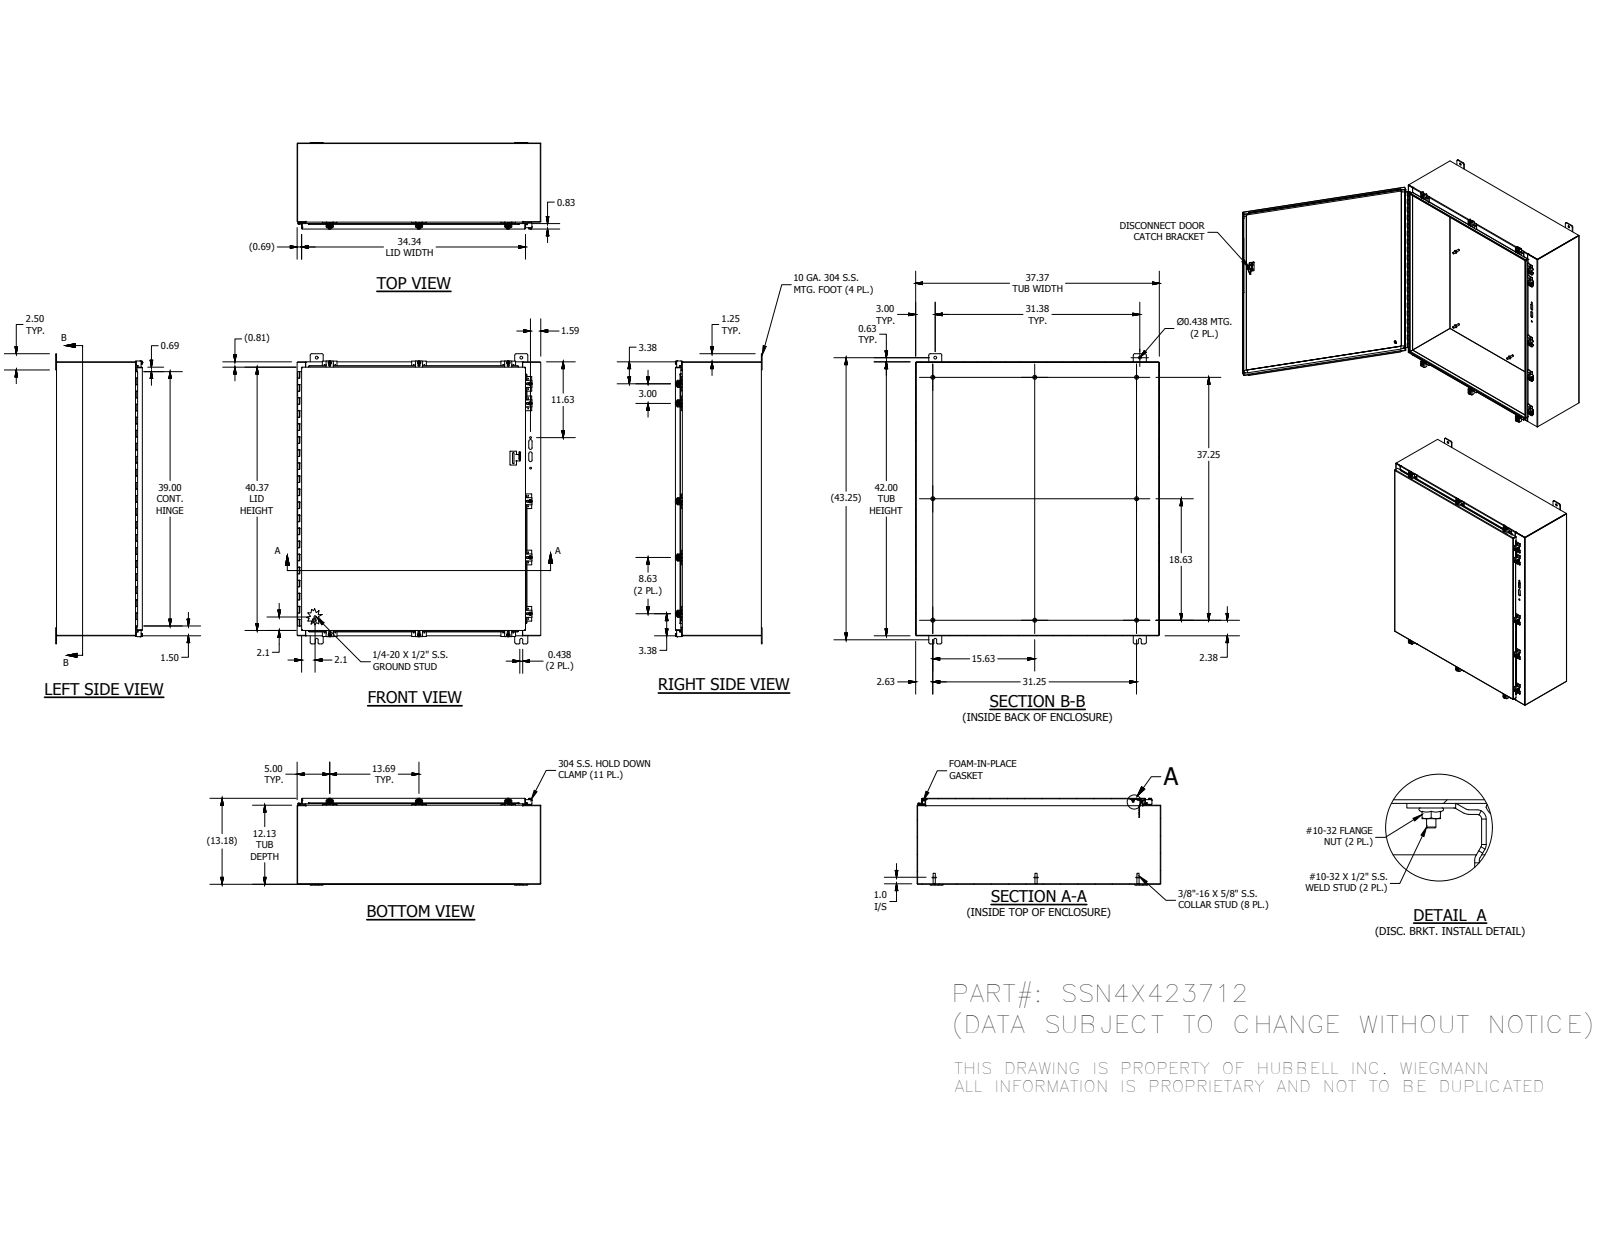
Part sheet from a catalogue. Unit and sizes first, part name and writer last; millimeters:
Units: millimetres
Overall size (bounding box): 1130.3 × 949.33 × 337.85
Round holes (diameter × count): ⌀2.79 ×22, ⌀5.36 ×11, ⌀7.16 ×11, ⌀11.13 ×4, ⌀3.96 ×2, ⌀7.14 ×2, ⌀3.17 ×1
Round bosses / shafts (diameter × count): ⌀15.88 ×19, ⌀6.35 ×13, ⌀13.21 ×11, ⌀8.89 ×11, ⌀5.04 ×11, ⌀0.76 ×10, ⌀8.38 ×8, ⌀8.56 ×3
Partial cylindrical surfaces — rounded edges, fillets, slot ends (radius × count): R0.76 ×89, R6.35 ×39, R3.17 ×27, R0.79 ×25, R3.62 ×22, R2.67 ×21, R1.59 ×17, R1.35 ×16
Main face-to-face distances: 1.88, 332.79, 330.91, 334.67, 1064.92, 1.87, 945.57, 947.45, 949.32, 947.44
Hole centre spacings: 1052.12, 22.26, 347.66, 368.39, 1099.97, 1101.58, 1114.53, 327.13
Volume: 7 149 000 mm³ · Surface area: 7 370 000 mm²
Bodies: 70 solids, 2365 faces (1207 planar, 670 cylindrical, 488 other)
Part name (STEP PRODUCT): SSN4X423712BLR; 38859; 34871; SSN4X4237LID (+8 more)
STEP written by: Autodesk Inventor 2016 (AUTOMOTIVE_DESIGN)
